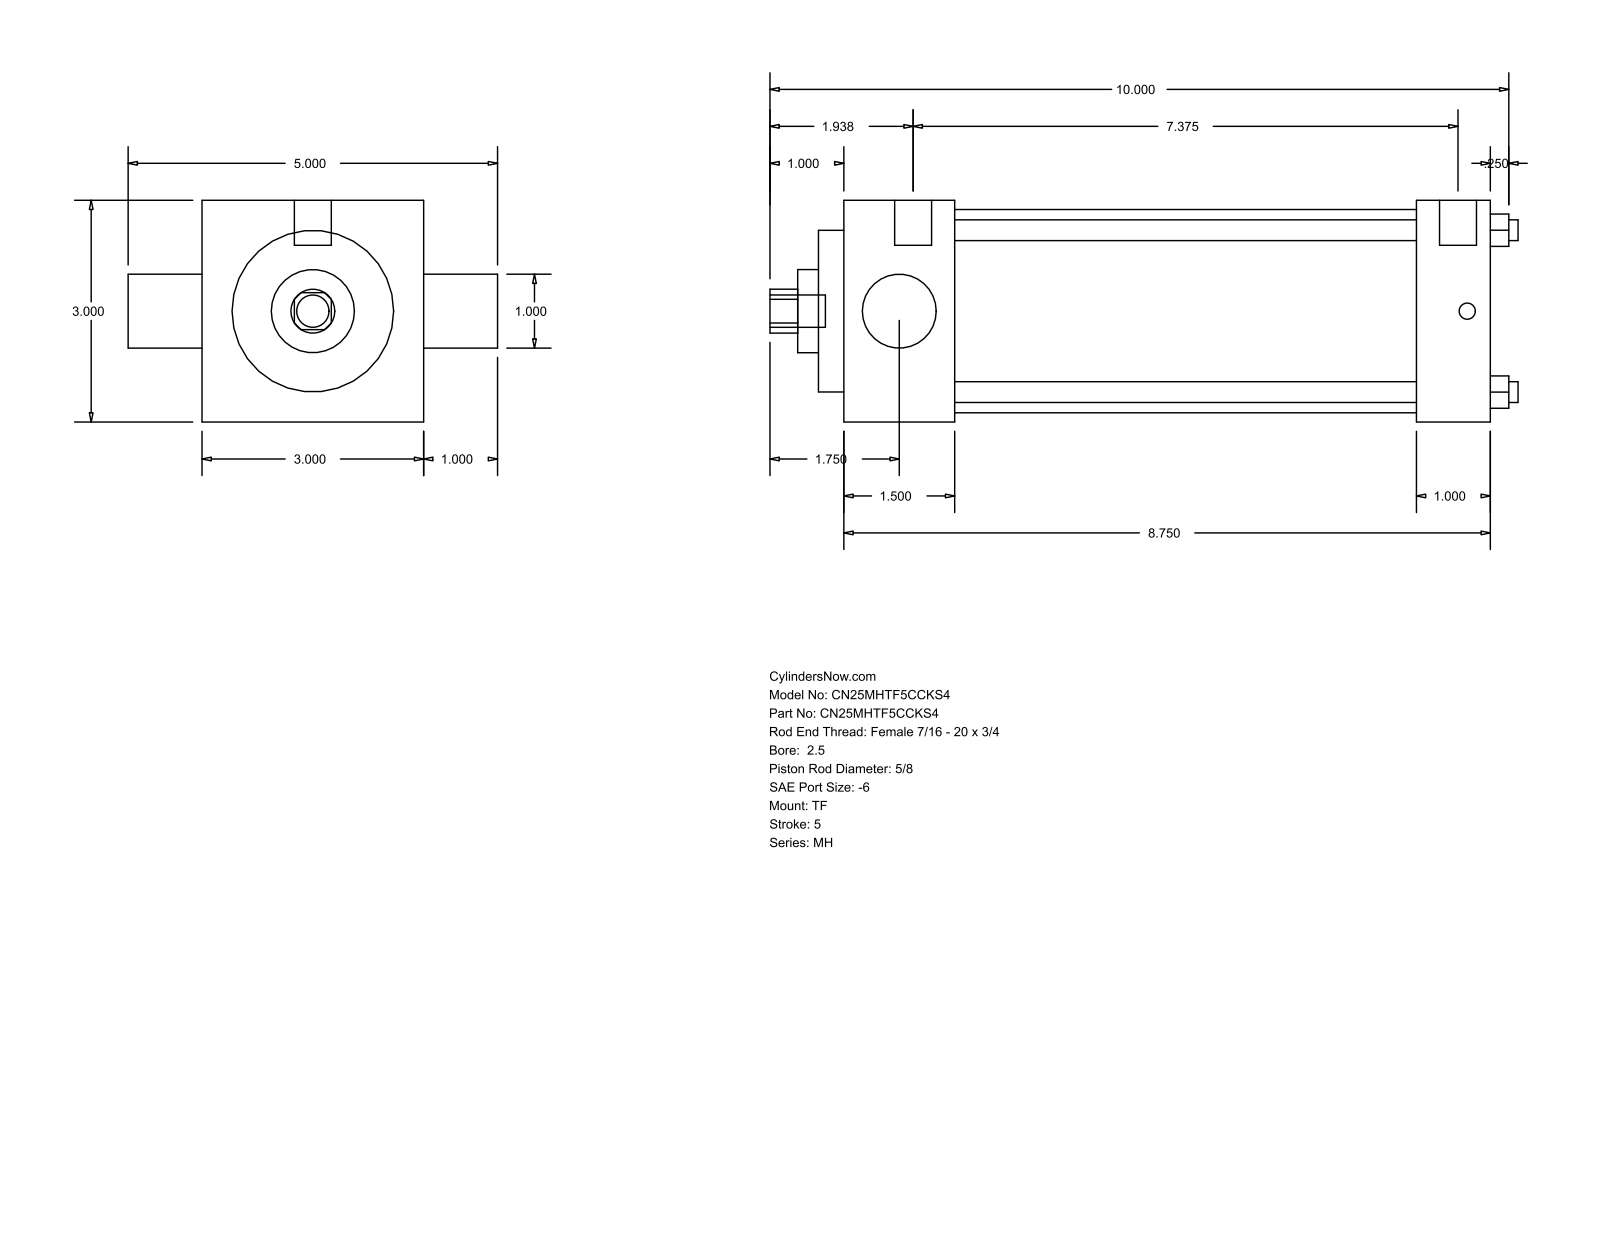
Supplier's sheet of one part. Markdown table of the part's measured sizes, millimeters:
| quantity | value |
| --- | --- |
| part name | MH_TF__0250_0.625 |
| STEP written by | GSSL Pune (CONFIG_CONTROL_DESIGN) |
| units | millimeters |
| bodies | 0 solids, 86 faces (61 planar, 25 cylindrical, 0 other) |
| overall size | 257.18 × 127 × 76.2 |
| round holes (diameter × count) | 7.14 × 4, 15.88 × 1, 25.4 × 1, 28.57 × 1, 55.55 × 1, 69.85 × 1 |
| round bosses / shafts (diameter × count) | 5.56 × 3, 12.7 × 2, 11.11 × 1 |
| partial cylindrical surfaces (radius × count) | 7.54 × 1 |
| main face-to-face distances | 76.2, 222.25, 25.4, 38.1, 184.15, 196.85, 158.75, 8.73, 46.83, 205.58 |
| hole center spacings | 39.33, 55.62, 78.66 |
